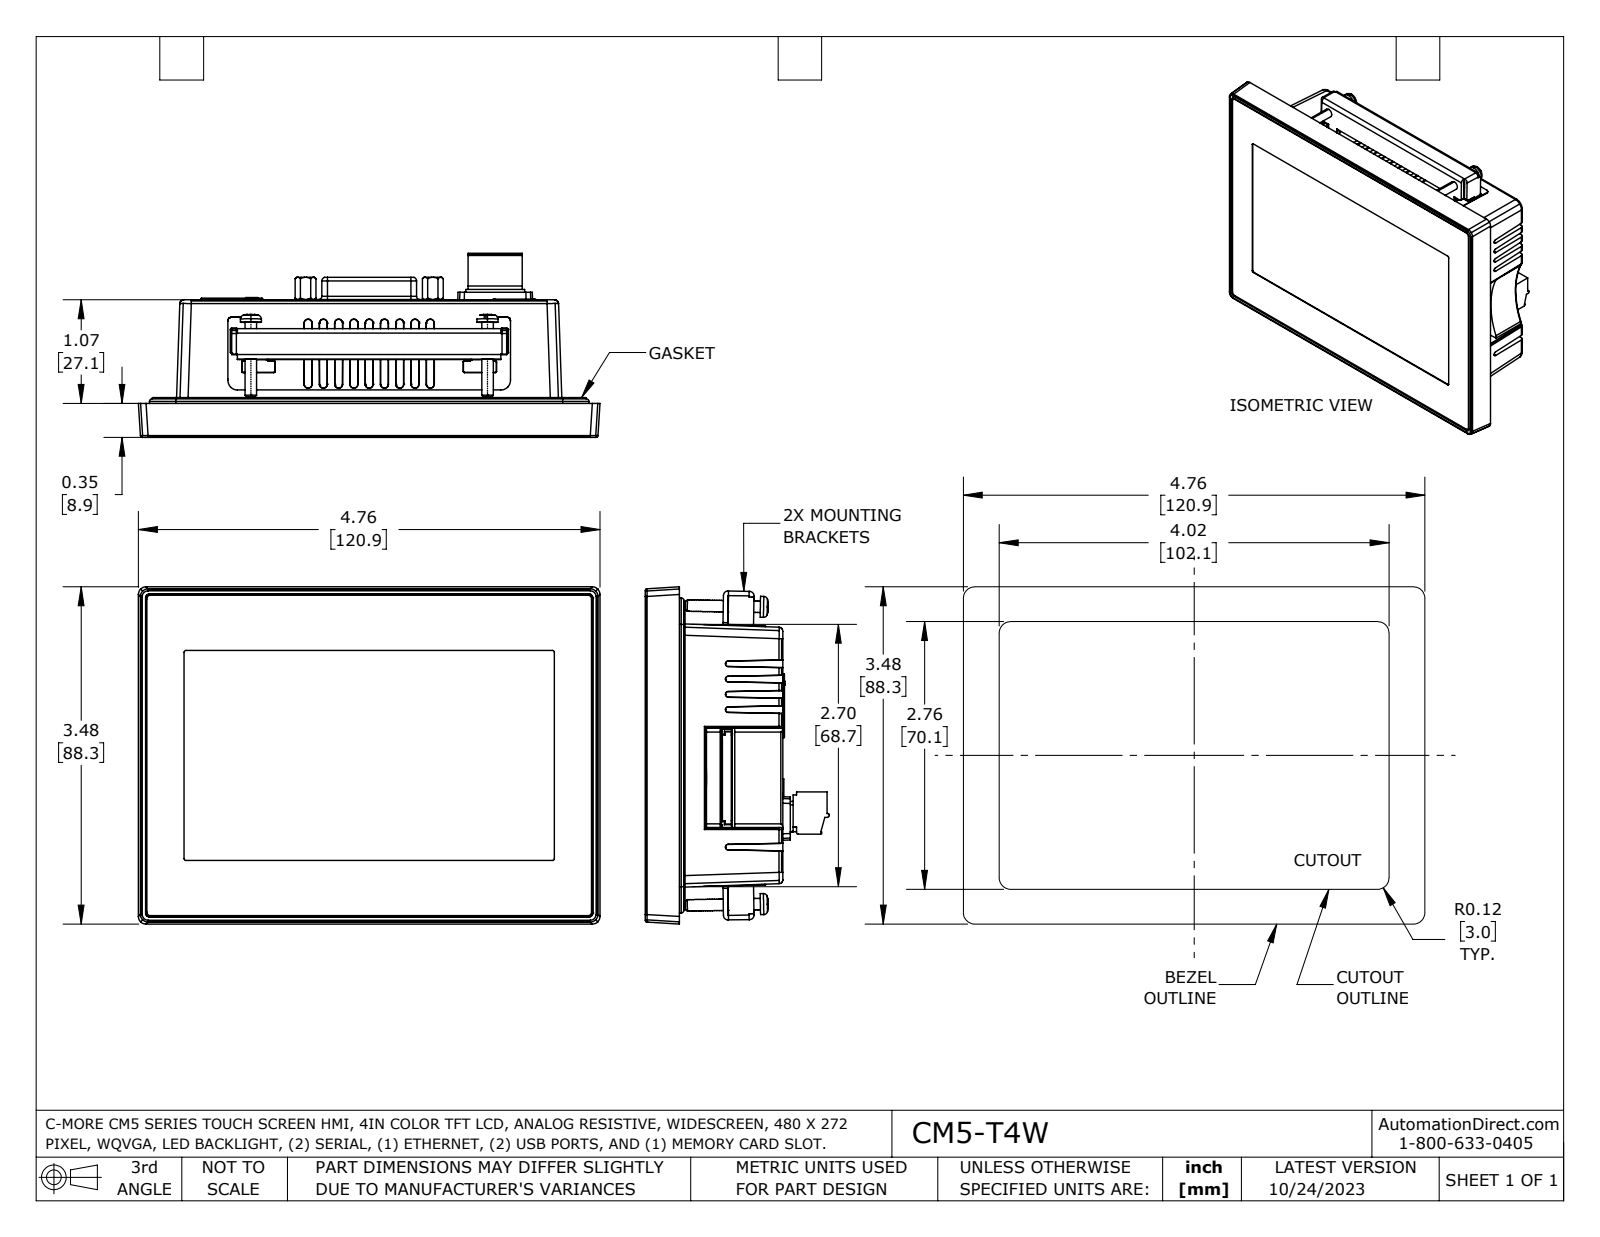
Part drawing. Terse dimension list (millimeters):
name: CM5-T4W_NEW
written by: SolidWorks 2021 (AUTOMOTIVE_DESIGN)
unit: mm
bodies: 1 solid, 2363 faces (1307 planar, 815 cylindrical, 241 other)
size: 120.9 × 88.3 × 48.2
volume: 280 100 mm³; area: 55 560 mm²
holes: 15× ⌀0.6, 15× ⌀1.5, 4× ⌀2.9, 4× ⌀3.1, 2× ⌀2.2
bosses: 6× ⌀0.5, 4× ⌀5.5, 4× ⌀3, 4× ⌀2.8, 1× ⌀0.5
rounds: 90× R0.3, 61× R0.5, 25× R1, 24× R0.2, 14× R0.6, 14× R0.7, 13× R0.8, 13× R0.8
face distances: 36, 35.7, 8.9, 27.1, 8.7, 1.2, 5.6, 6.8, 1.7, 7.3
hole spacings: 3.1, 2.8, 5.5, 8.3, 5, 7.5, 11.1, 5
